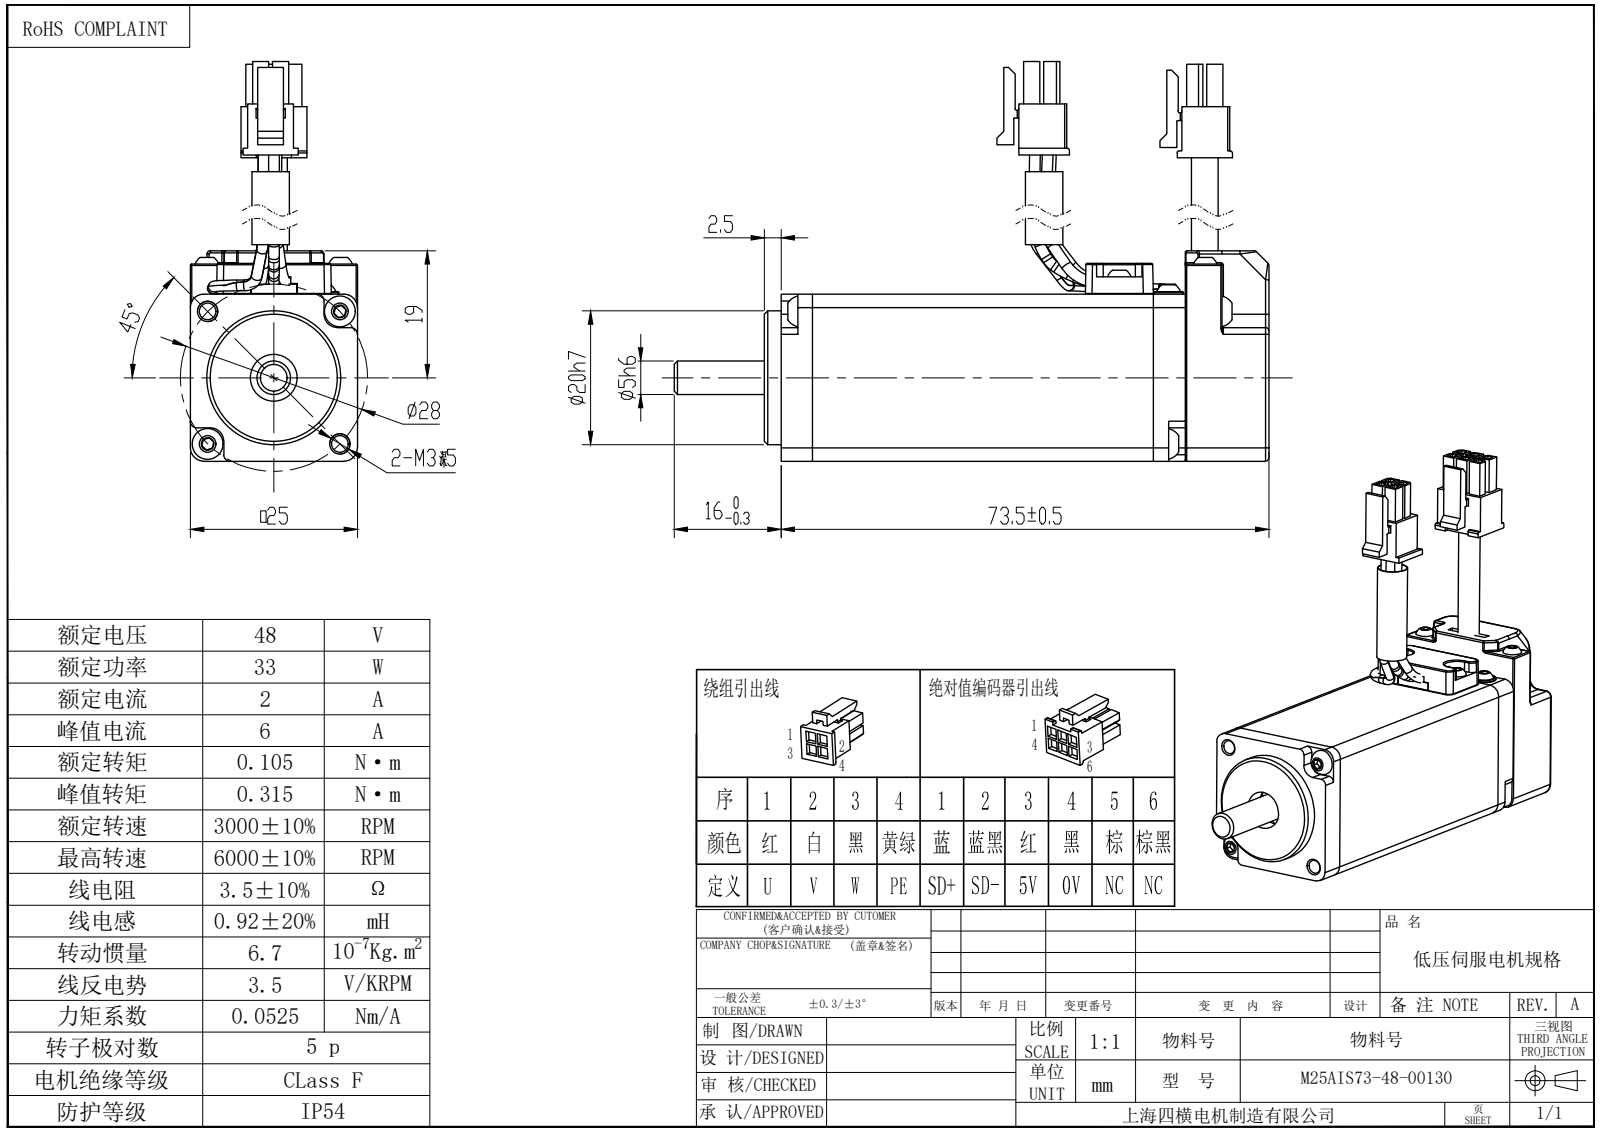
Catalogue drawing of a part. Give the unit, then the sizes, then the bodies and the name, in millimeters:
Units: millimetres
Overall size (bounding box): 89 × 68.9 × 25
Round holes (diameter × count): ⌀2.5 ×5, ⌀1.6 ×3, ⌀2 ×2, ⌀3 ×2, ⌀5.4 ×1, ⌀7 ×1, ⌀9 ×1, ⌀9.5 ×1, ⌀11.5 ×1, ⌀12 ×1, ⌀22.8 ×1
Round bosses / shafts (diameter × count): ⌀1.6 ×17, ⌀2 ×3, ⌀23 ×1, ⌀20 ×1, ⌀17.7 ×1, ⌀5.6 ×1, ⌀5 ×1, ⌀4 ×1
Partial cylindrical surfaces — rounded edges, fillets, slot ends (radius × count): R0.2 ×37, R0.5 ×17, R0.3 ×15, R1 ×15, R2 ×8, R0.25 ×4, R0.15 ×2, R0.28 ×2
Main face-to-face distances: 25, 12.5, 1, 1.5, 4.8, 51, 11, 50, 17.3, 15.8
Hole centre spacings: 14, 19.8, 13.35, 20.93, 28, 6.04, 7.45, 12.76
Volume: 25 909 mm³ · Surface area: 24 103 mm²
Bodies: 25 solids, 1062 faces (472 planar, 267 cylindrical, 323 other)
Part name (STEP PRODUCT): 25前端盖; M25AIS73-48-00130; 25动力线; PE (+8 more)
STEP written by: SolidWorks 2020 (AUTOMOTIVE_DESIGN)
